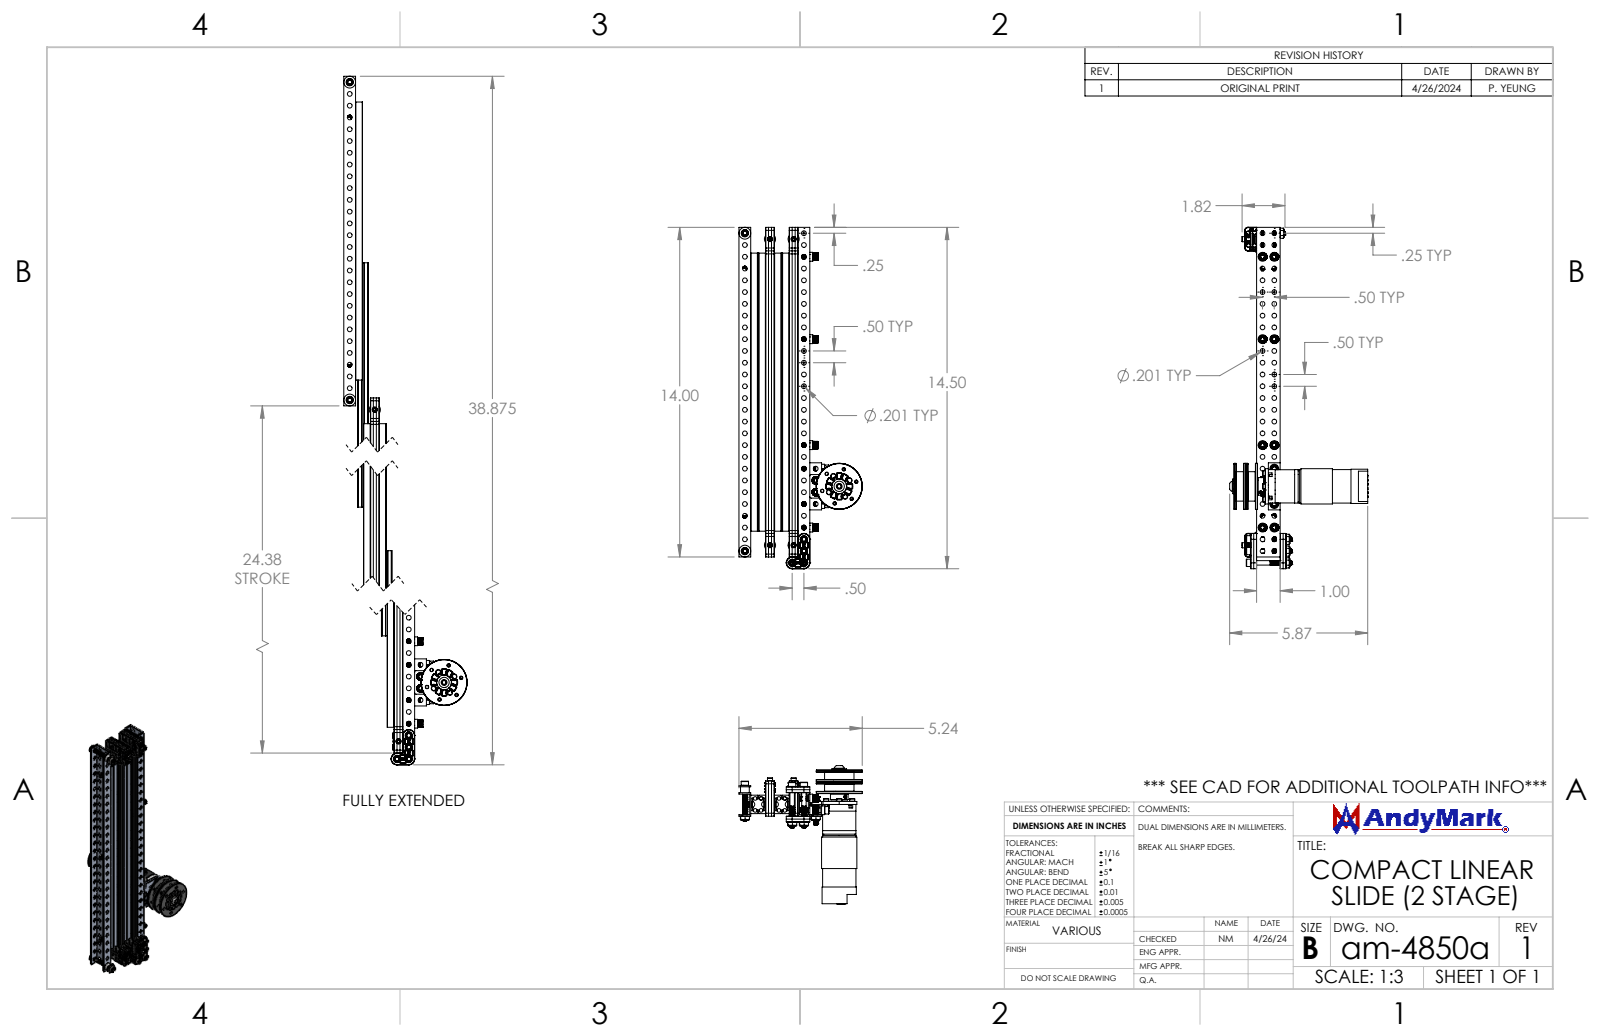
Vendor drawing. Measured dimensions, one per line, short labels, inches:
name: SAR330_108; am-4836 3mm ID x 12mm OD x 4mm Thick V Groove Bearing; Shim; NeveRest Orbital 2 Stage Gearbox 6mm D (+8 more)
written by: SolidWorks 2024 (AUTOMOTIVE_DESIGN)
unit: in
bodies: 245 solids, 30093 faces (5598 planar, 10500 cylindrical, 13995 other)
size: 14.5 × 5.875 × 5.236
volume: 27.6 in³; area: 630.7 in²
holes: 122× ⌀0.201, 80× ⌀0.164, 20× ⌀0.161, 20× ⌀0.239, 18× ⌀0.125, 13× ⌀0.125, 10× ⌀0.098, 10× ⌀0.194, 5× ⌀0.315, 4× ⌀0.171, 4× ⌀0.262, 4× ⌀0.285
bosses: 21× ⌀0.19, 13× ⌀0.118, 12× ⌀0.375, 12× ⌀0.217, 10× ⌀0.313, 10× ⌀0.312, 10× ⌀0.093, 5× ⌀0.472
rounds: 2752× R0.01, 80× R0.008, 34× R0.064, 32× R0.031, 20× R0.082, 16× R0.075, 12× R0.125, 8× R0.089
face distances: 1.005, 0.063, 0.5, 0.437, 0.63, 0.106, 0.894, 0.375, 0.055, 0.575
hole spacings: 0.5, 1, 1.5, 2, 2.5, 3, 3.5, 4
